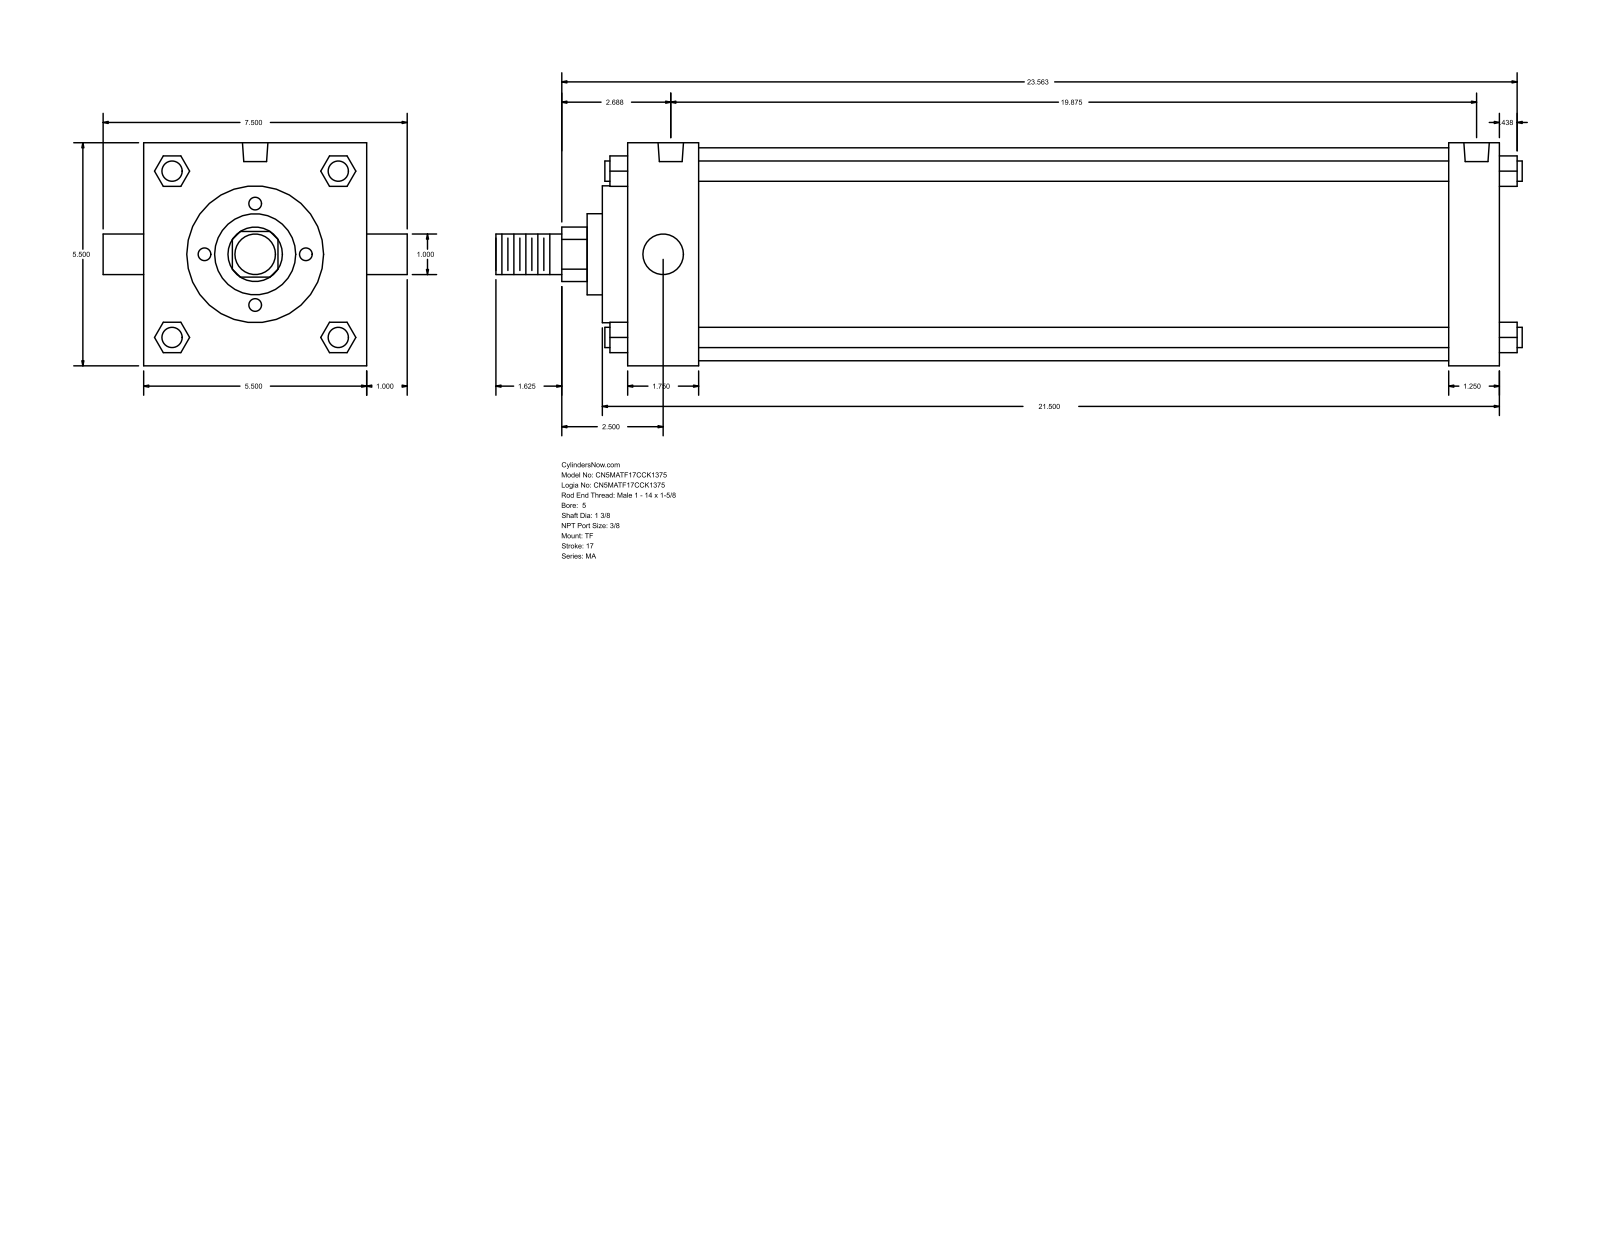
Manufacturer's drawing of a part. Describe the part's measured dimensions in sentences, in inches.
The part is named "MA_TF__0500_1.375". Its 3-D file was written by "GSSL Pune (CONFIG_CONTROL_DESIGN)". It is 0 solids with 122 faces: 93 planar, 29 cylindrical and 0 other. Overall it measures 25.313 by 7.5 by 5.5 inches. Round holes: 3 of diameter 0.437, 2 of diameter 0.627. Round bosses or shafts: 4 of diameter 0.5, 2 of diameter 1, 1 of diameter 5.25, 1 of diameter 3.375, 1 of diameter 2, 1 of diameter 1.375. Partial cylindrical surfaces (rounded edges, fillets, slot ends): 1 of radius 0.672. The main face-to-face distances are 5.5, 21.5, 20.25, 1.25, 1.75, 18.5, 19.75, 0.625, 2.375, 20.875. The hole center spacings are 0.187, 0.188, 19.5, 19.687, 19.688, 19.875.
